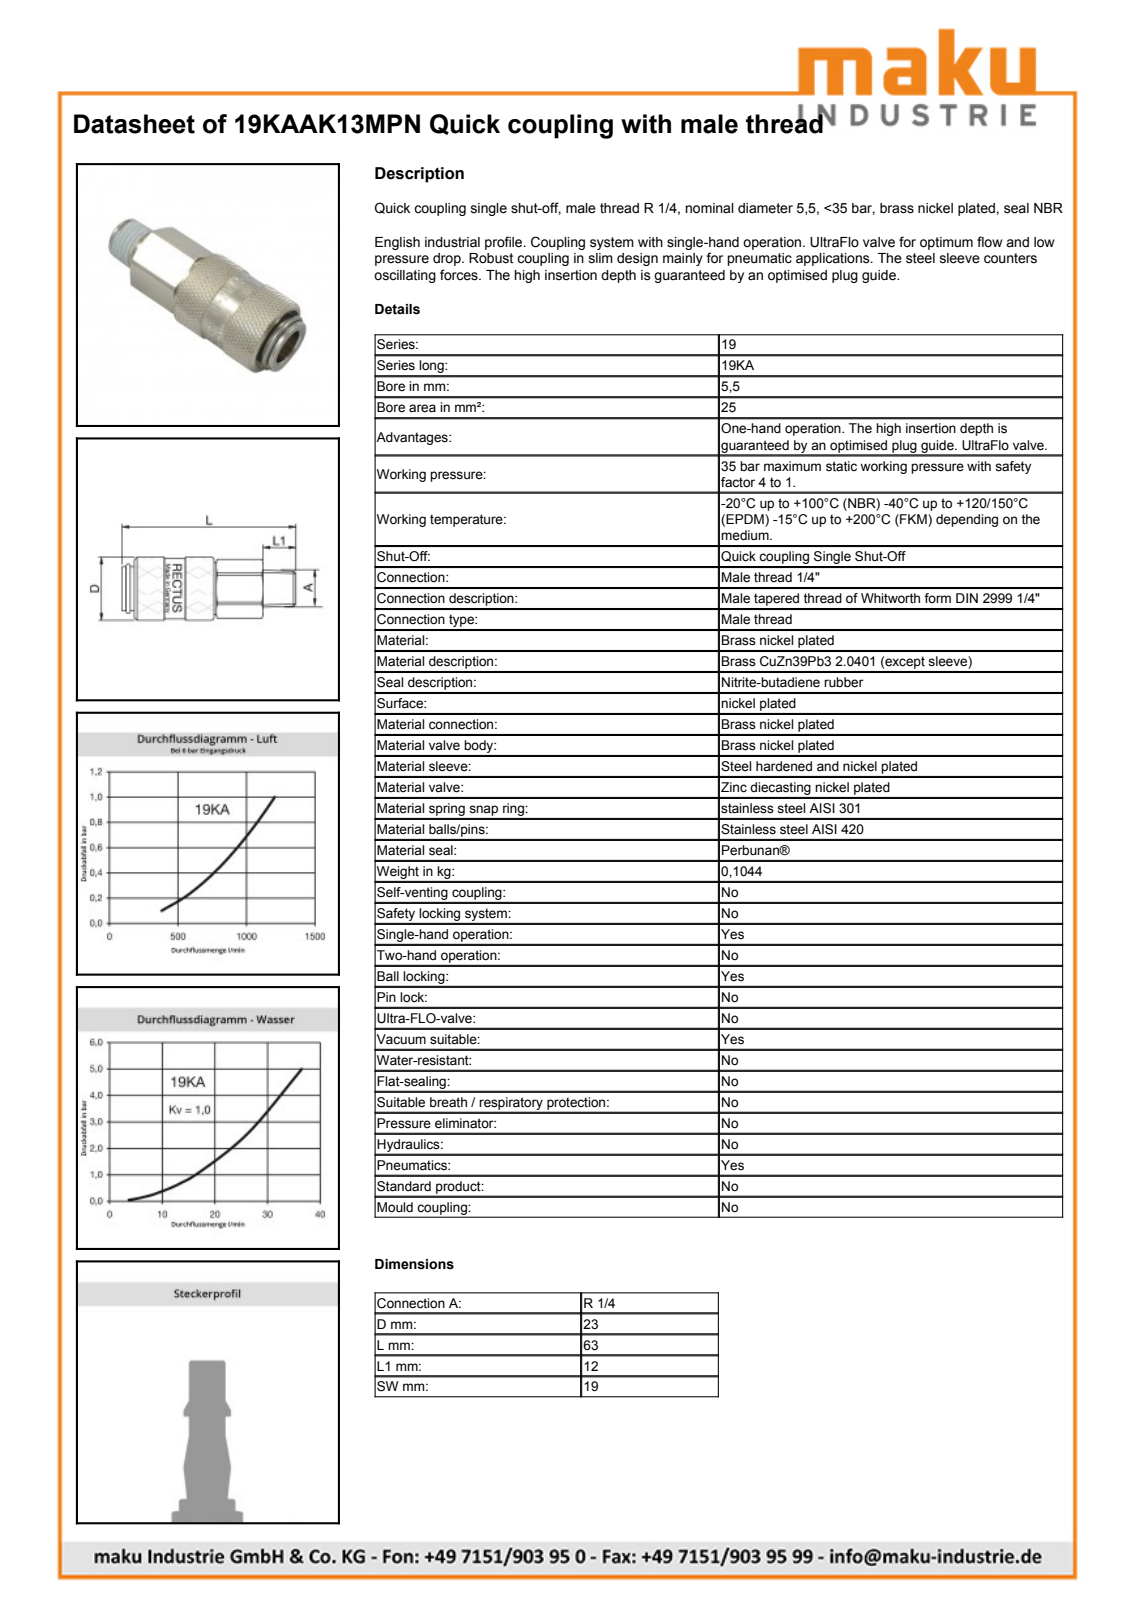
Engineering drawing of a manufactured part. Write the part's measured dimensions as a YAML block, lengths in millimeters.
part_name: "D112937"
step_written_by: "Autodesk Inventor 2013 (AUTOMOTIVE_DESIGN)"
units: millimeters
bodies: {solids: 1, faces: 310, planar: 124, cylindrical: 38, other: 148}
overall_size: [63.3, 23, 23]
volume: 19764
surface_area: 5516
round_holes:
  - {diameter: 15.46, count: 1}
  - {diameter: 21, count: 1}
round_bosses_or_shafts:
  - {diameter: 23, count: 1}
  - {diameter: 22, count: 1}
  - {diameter: 20.34, count: 1}
  - {diameter: 18.95, count: 1}
  - {diameter: 16, count: 1}
  - {diameter: 15.43, count: 1}
  - {diameter: 15, count: 1}
partial_cylinders:
  - {radius: 10.7, count: 1}
  - {radius: 10.9, count: 1}
face_to_face_distances: [19, 4.48, 46.82, 51.3, 12, 58.82, 63.3, 29.82, 17.82, 29]
